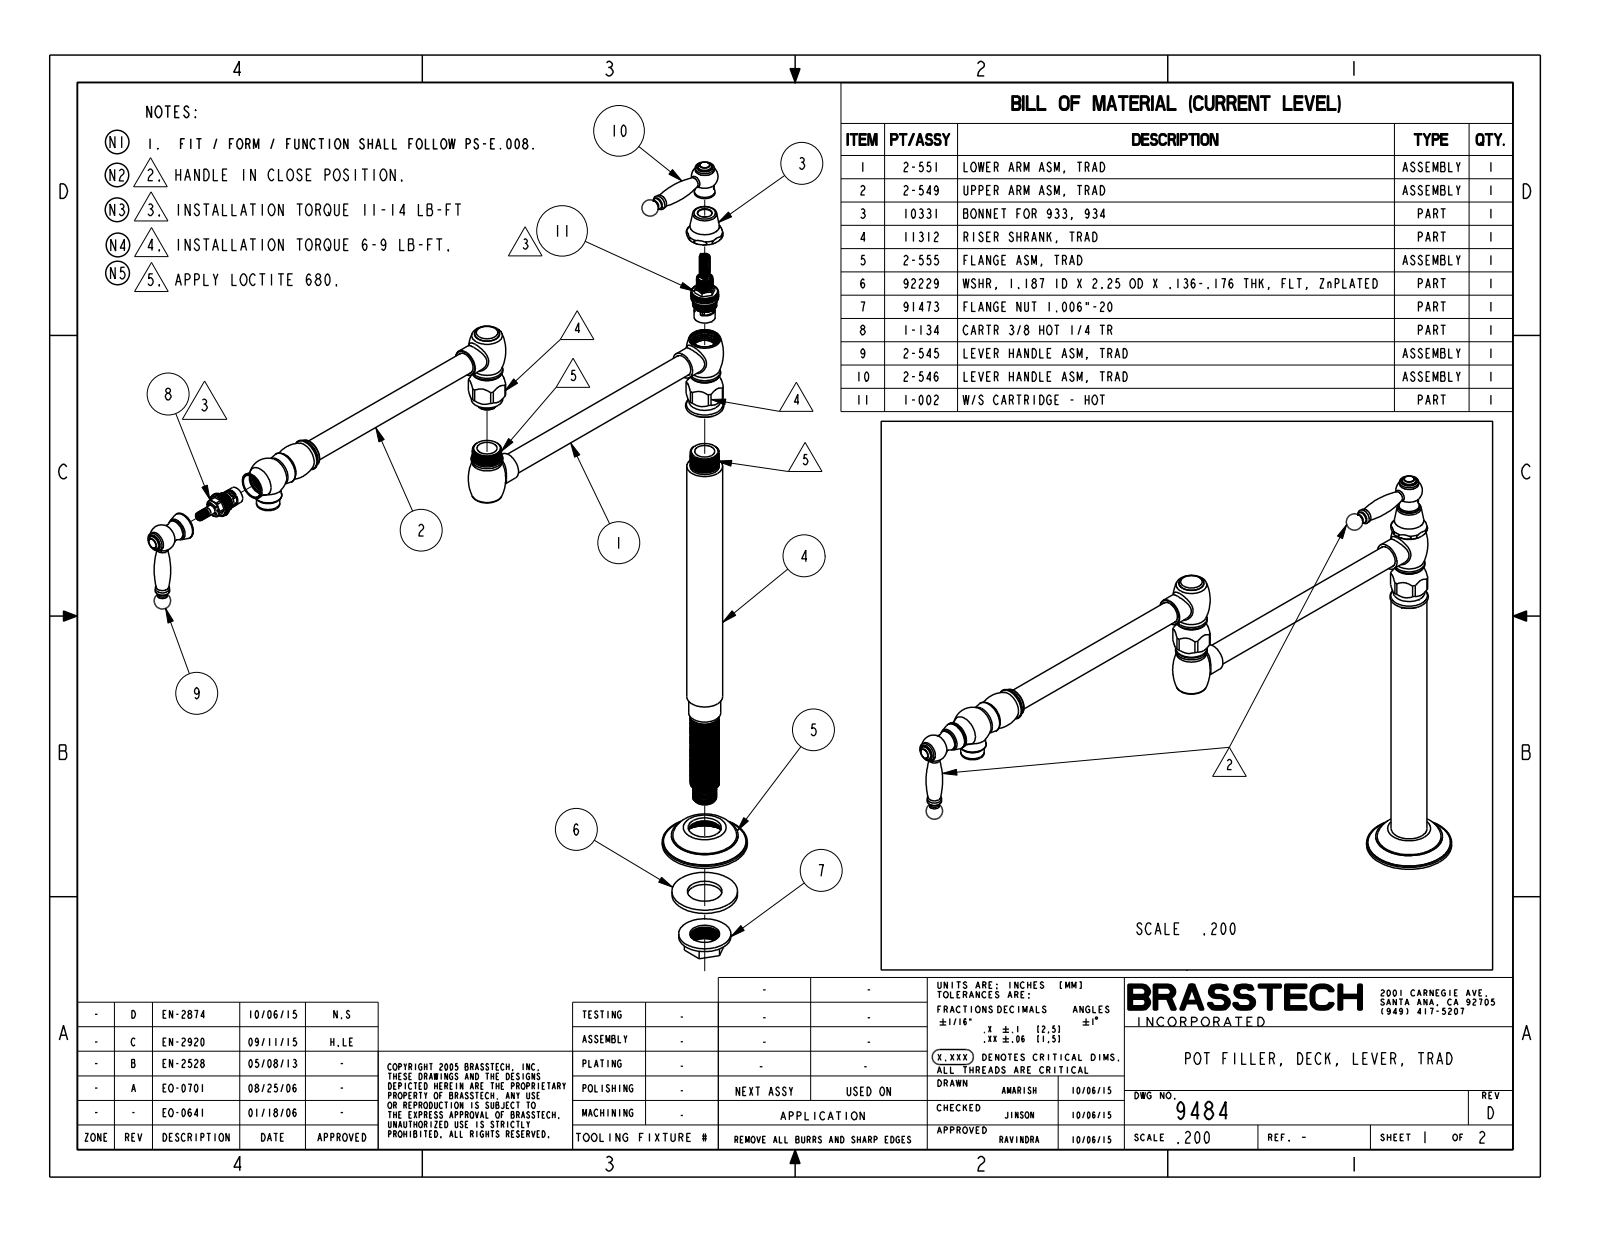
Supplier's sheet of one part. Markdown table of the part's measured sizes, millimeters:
| quantity | value |
| --- | --- |
| part name | 11310; 91423; 11311; 91424 (+8 more) |
| STEP written by | PRO/ENGINEER BY PARAMETRIC TECHNOLOGY CORPORATION, 2009300 (CONFIG_CONTROL_DESIGN) |
| units | millimeters |
| bodies | 41 solids, 2961 faces (709 planar, 1176 cylindrical, 1076 other) |
| overall size | 631.4 × 507.9 × 74.2 |
| volume | 419 800 mm³ |
| surface area | 300 300 mm² |
| round holes (diameter × count) | 17.5 × 3, 3.3 × 2, 5 × 2, 5.2 × 2, 6.7 × 2, 10.2 × 2, 12.7 × 2, 14.3 × 2, 15.7 × 2, 17.8 × 2, 19.3 × 2, 20.2 × 2 |
| round bosses / shafts (diameter × count) | 23.9 × 4, 4.2 × 3, 25.4 × 2, 23.8 × 2, 23.7 × 2, 22 × 2, 20.1 × 2, 19.1 × 2 |
| partial cylindrical surfaces (radius × count) | 1 × 7, 2 × 6, 1.4 × 2, 1.6 × 2, 3.7 × 2, 7.6 × 2, 16.5 × 2, 3.8 × 1 |
| main face-to-face distances | 4.6, 29.7, 29.8, 17.5, 13, 74.7, 12.7, 29.7, 232.5, 262.2 |
| hole center spacings | 5.8, 11.4, 17.2, 18.7, 35.7, 47.1, 57.4, 74.7 |
